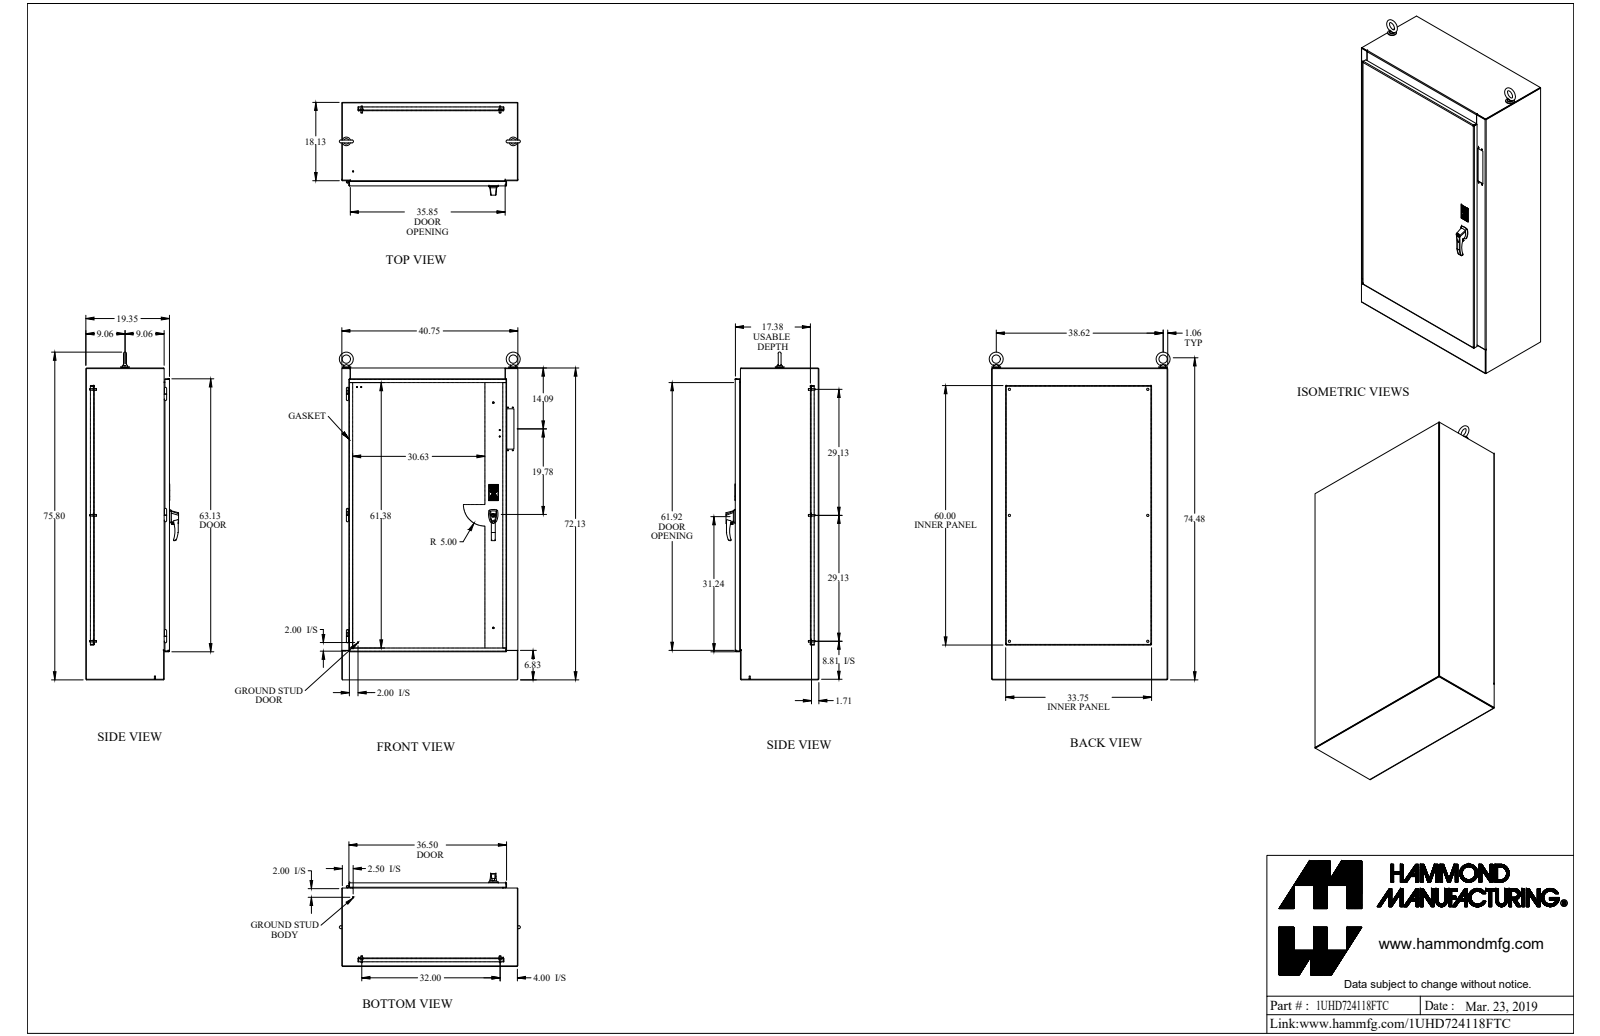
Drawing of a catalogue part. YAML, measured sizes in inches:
part_name: "1UHD724118FTC"
step_written_by: "SolidWorks 2018 (AUTOMOTIVE_DESIGN)"
units: inches
bodies: {solids: 102, faces: 1773, planar: 978, cylindrical: 482, other: 313}
overall_size: [75.799, 41.872, 21.464]
volume: 1752
surface_area: 28062
round_holes:
  - {diameter: 0.307, count: 7}
  - {diameter: 0.35, count: 7}
  - {diameter: 0.281, count: 6}
  - {diameter: 0.445, count: 6}
  - {diameter: 0.563, count: 6}
  - {diameter: 0.196, count: 5}
  - {diameter: 0.25, count: 3}
  - {diameter: 0.313, count: 3}
  - {diameter: 0.167, count: 2}
  - {diameter: 0.257, count: 2}
  - {diameter: 0.28, count: 2}
  - {diameter: 0.39, count: 2}
round_bosses_or_shafts:
  - {diameter: 0.25, count: 10}
  - {diameter: 1, count: 8}
  - {diameter: 0.65, count: 6}
  - {diameter: 0.375, count: 6}
  - {diameter: 0.33, count: 6}
  - {diameter: 0.281, count: 4}
  - {diameter: 0.188, count: 4}
  - {diameter: 0.625, count: 3}
partial_cylinders:
  - {radius: 0.06, count: 39}
  - {radius: 0.185, count: 28}
  - {radius: 0.5, count: 25}
  - {radius: 0.125, count: 22}
  - {radius: 0.017, count: 16}
  - {radius: 0.032, count: 12}
  - {radius: 0.13, count: 8}
  - {radius: 0.318, count: 7}
face_to_face_distances: [0.125, 0.125, 17.413, 19.225, 19.1, 19.35, 19.224, 1.937, 1.812, 17.288]
hole_center_spacings: [43.27, 32, 1, 1.125, 1.126, 1.287, 2, 7.5]
